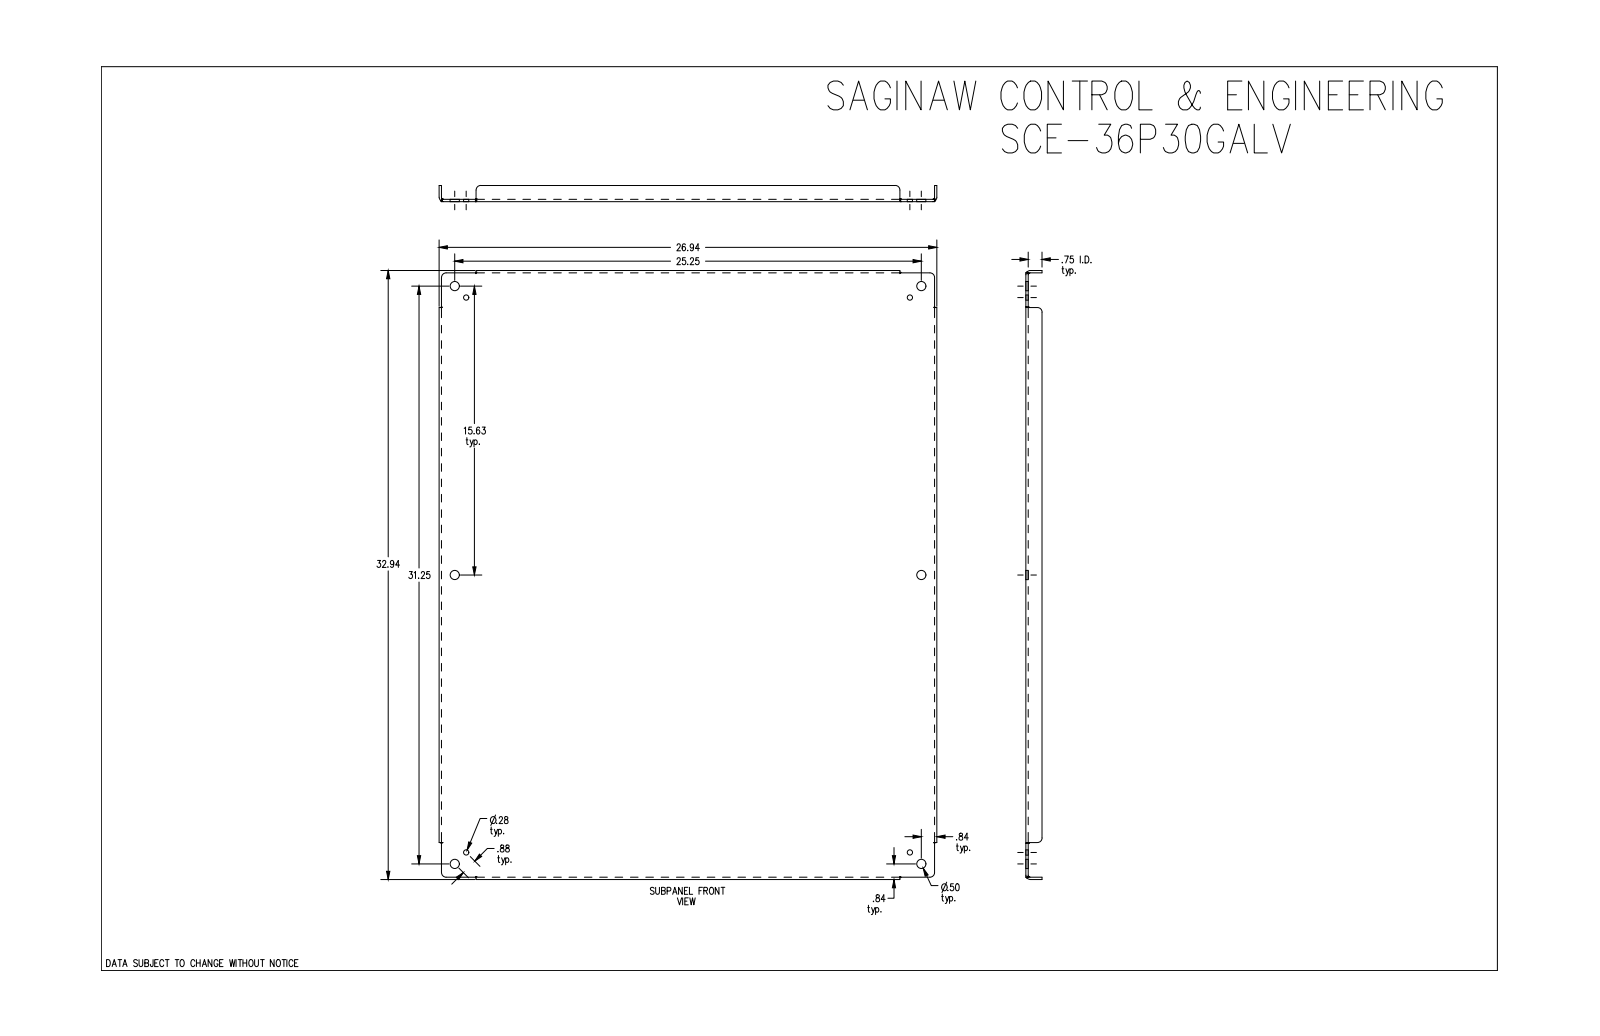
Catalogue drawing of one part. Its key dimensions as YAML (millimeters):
part_name: "SCE-36P30GALV"
step_written_by: "SolidWorks 2019 (CONFIG_CONTROL_DESIGN)"
units: millimeters
bodies: {solids: 1, faces: 84, planar: 30, cylindrical: 30, other: 24}
overall_size: [836.6, 684.2, 22.2]
volume: 1953000
surface_area: 1242000
round_holes:
  - {diameter: 12.7, count: 6}
  - {diameter: 7.1, count: 4}
partial_cylinders:
  - {radius: 6.4, count: 8}
  - {radius: 2.8, count: 4}
  - {radius: 6, count: 4}
face_to_face_distances: [3.2, 3.2, 681.1, 833.5, 677.8, 684.2, 830.2, 836.6, 19.1, 22.2]
hole_center_spacings: [22.2, 381.5, 396.9, 625.8, 732.6, 754.2, 778.2, 998.4]
